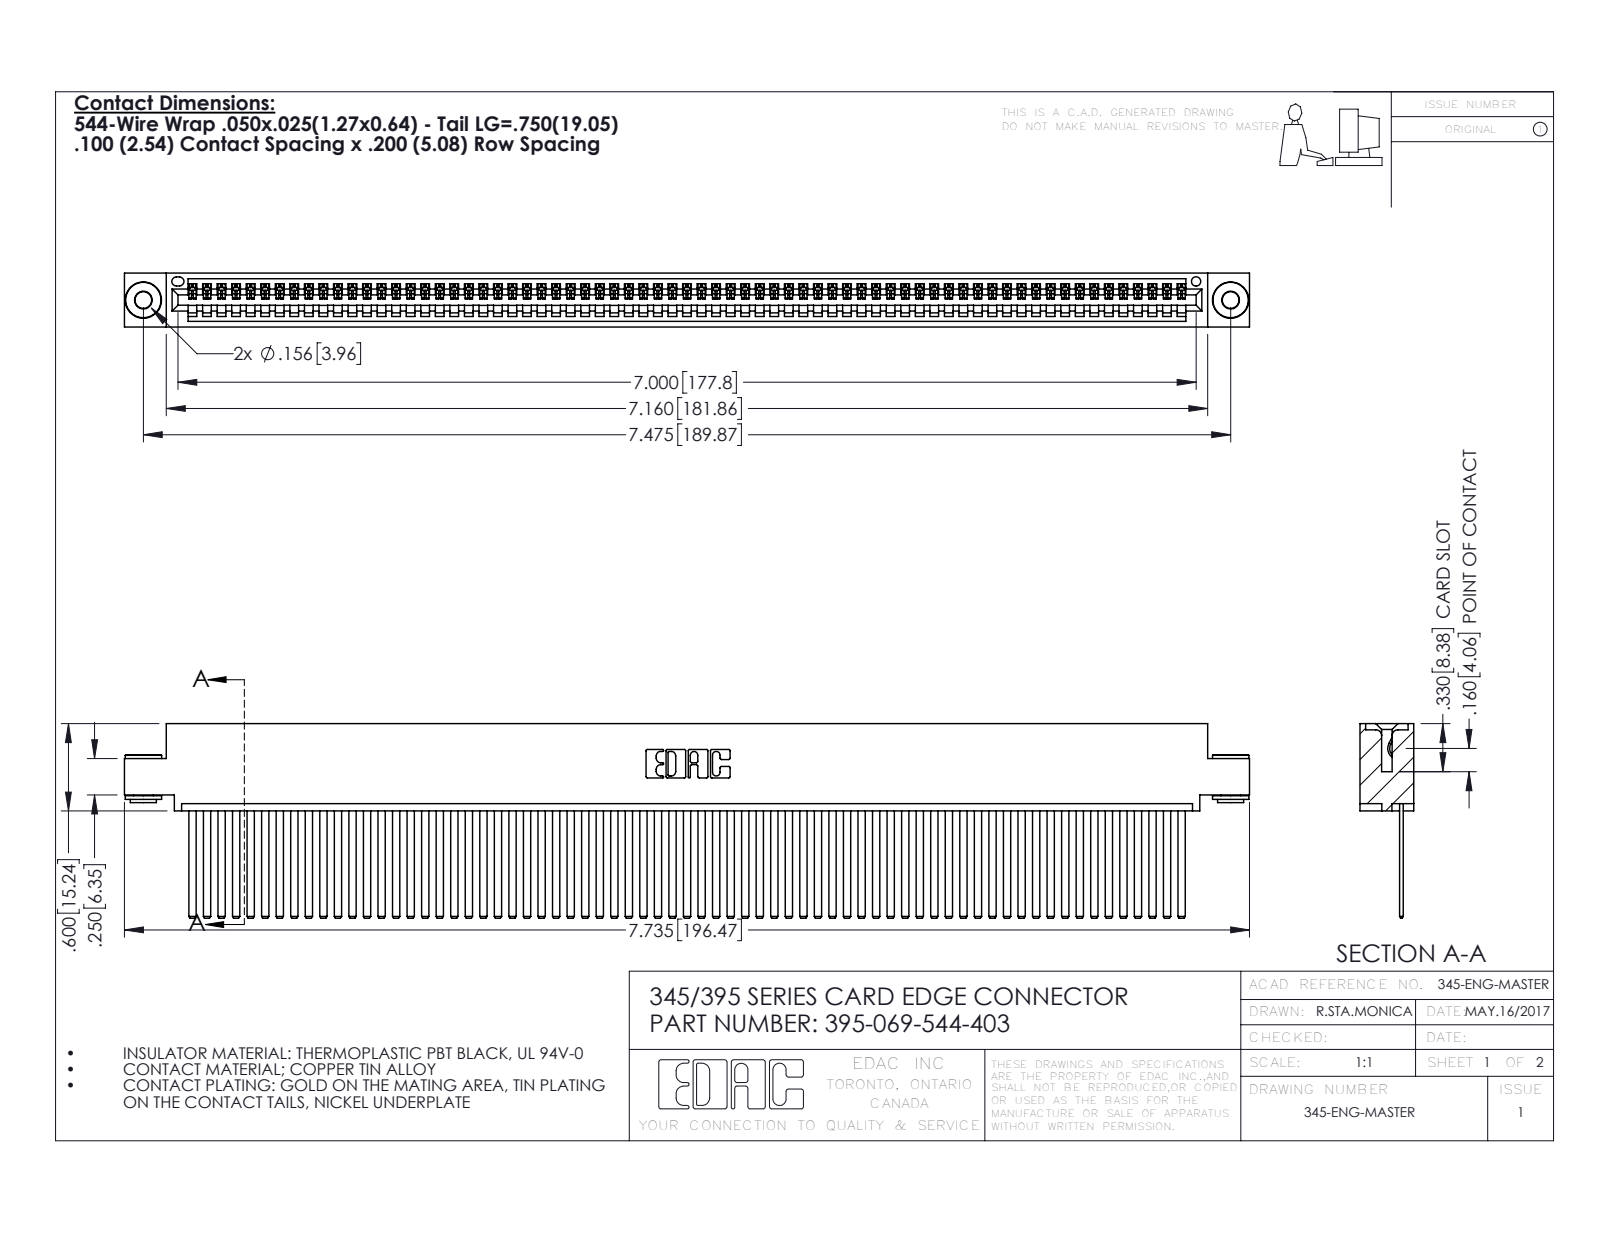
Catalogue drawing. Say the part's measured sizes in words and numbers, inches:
The part is named "345 Part_0.110 Offset - 0.156 Dia-TH; 395-069-544-403; 345-250-002_345-250-002-102; 345-292-001_345-293-144". Its 3-D file was written by "SolidWorks 2016 (CONFIG_CONTROL_DESIGN)". It is 72 solids with 3756 faces: 2578 planar, 1170 cylindrical and 8 other. Overall it measures 7.735 by 1.337 by 0.37 inches. Its volume is 1.198 cubic inches and its surface area 45.17 square inches. Round holes: 2 of diameter 0.116, 2 of diameter 0.156, 1 of diameter 0.064. Round bosses or shafts: 2 of diameter 0.25, 2 of diameter 0.18, 2 of diameter 0.136. Partial cylindrical surfaces (rounded edges, fillets, slot ends): 138 of radius 0.006, 22 of radius 0.01, 6 of radius 0.007, 6 of radius 0.031, 3 of radius 0.026, 2 of radius 0.031, 2 of radius 0.04, 1 of radius 0.014. The main face-to-face distances are 0.072, 0.298, 0.025, 0.098, 0.272, 0.37, 0.2, 0.225, 0.149, 0.072. The hole center spacings are 0.27, 7.239, 7.475.
